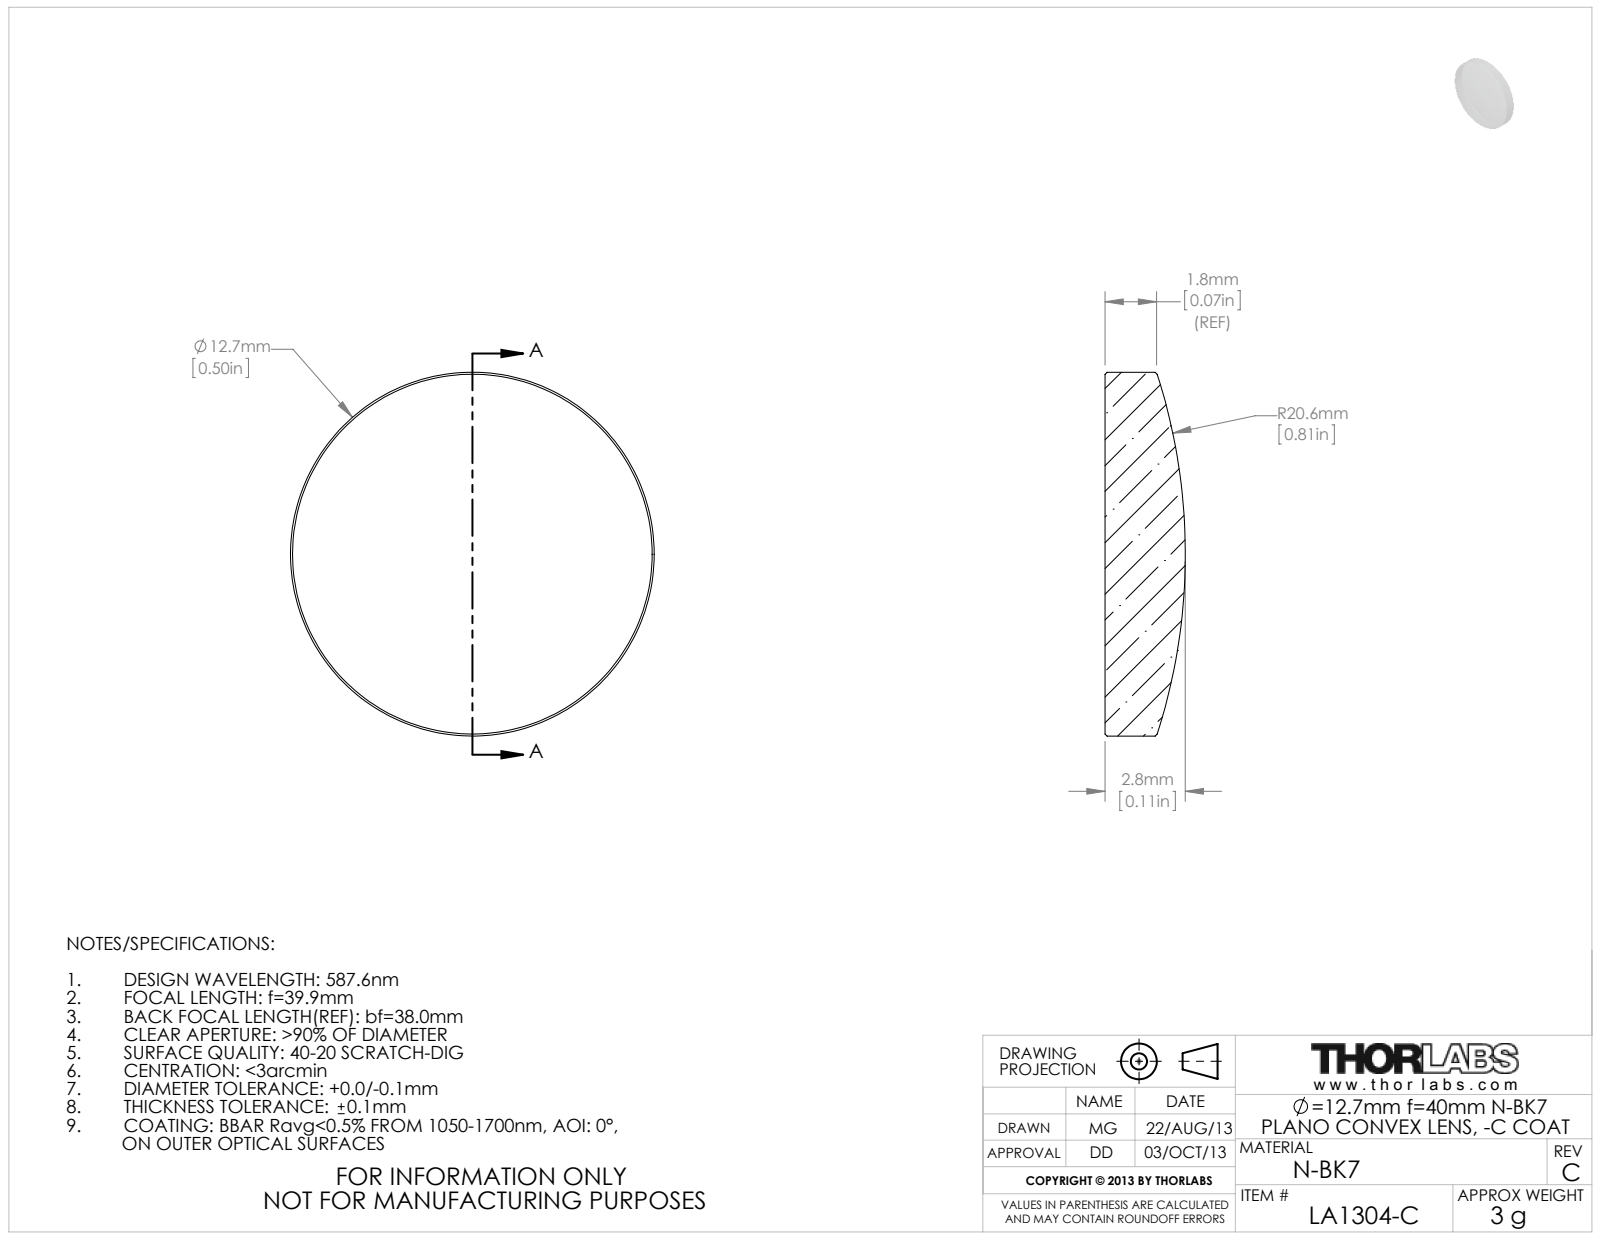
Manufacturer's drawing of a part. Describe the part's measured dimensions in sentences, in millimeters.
The part is named "4570-E0W". Its 3-D file was written by "SolidWorks 2009 (AUTOMOTIVE_DESIGN)". It is 1 solid with 5 faces: 1 planar, 2 cylindrical and 2 other. Overall it measures 12.7 by 12.7 by 2.8 millimeters. Its volume is 292 cubic millimeters and its surface area 328 square millimeters. Round bosses or shafts: 1 of diameter 12.7.
